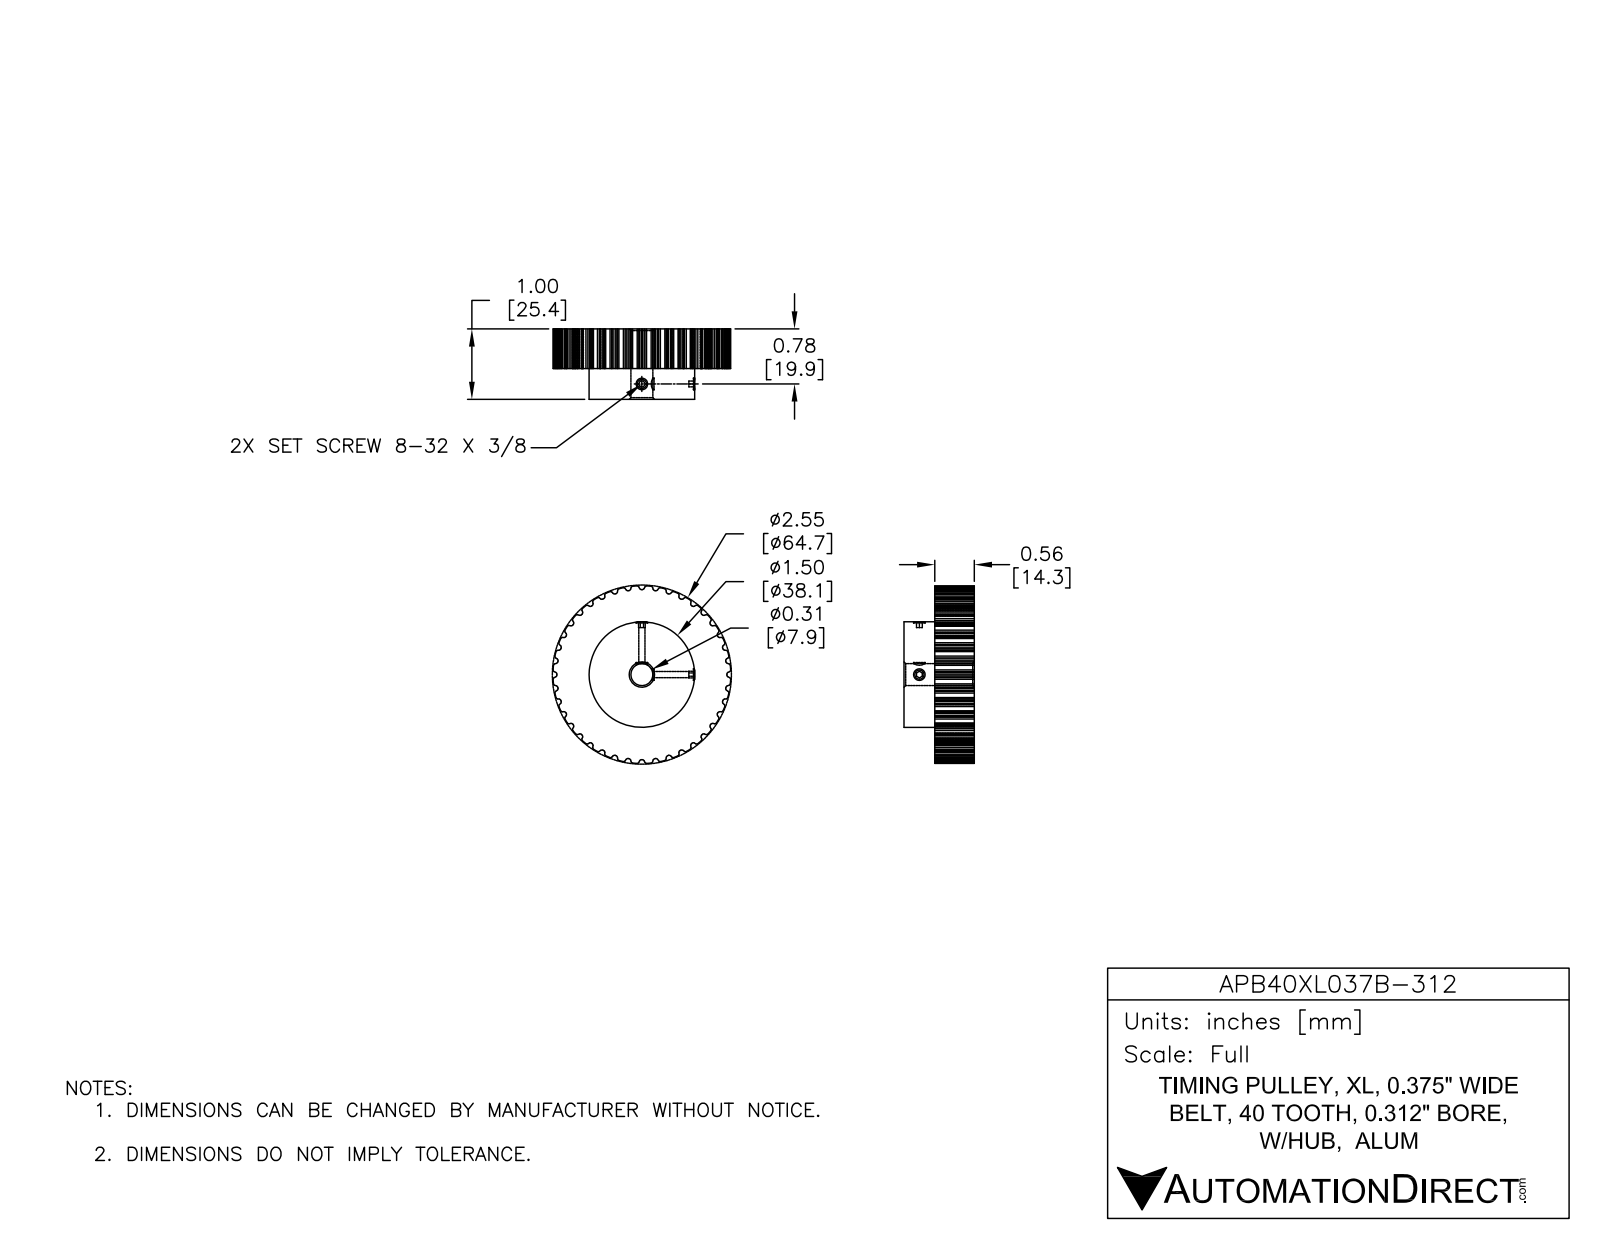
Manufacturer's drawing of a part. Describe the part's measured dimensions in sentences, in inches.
The part is named "APB40XL037B-312". Its 3-D file was written by "SolidWorks 2014 (AUTOMOTIVE_DESIGN)". It is 1 solid with 370 faces: 83 planar, 277 cylindrical and 10 other. Overall it measures 2.526 by 2.526 by 1 inches. Its volume is 3.405 cubic inches and its surface area 18.62 square inches. Round holes: 2 of diameter 0.088, 1 of diameter 0.313. Round bosses or shafts: 1 of diameter 1.5. Partial cylindrical surfaces (rounded edges, fillets, slot ends): 160 of radius 0.015, 1 of radius 1.208, 1 of radius 1.263. The main face-to-face distances are 0.56, 1, 0.44, 0.976, 0.974, 0.975.
